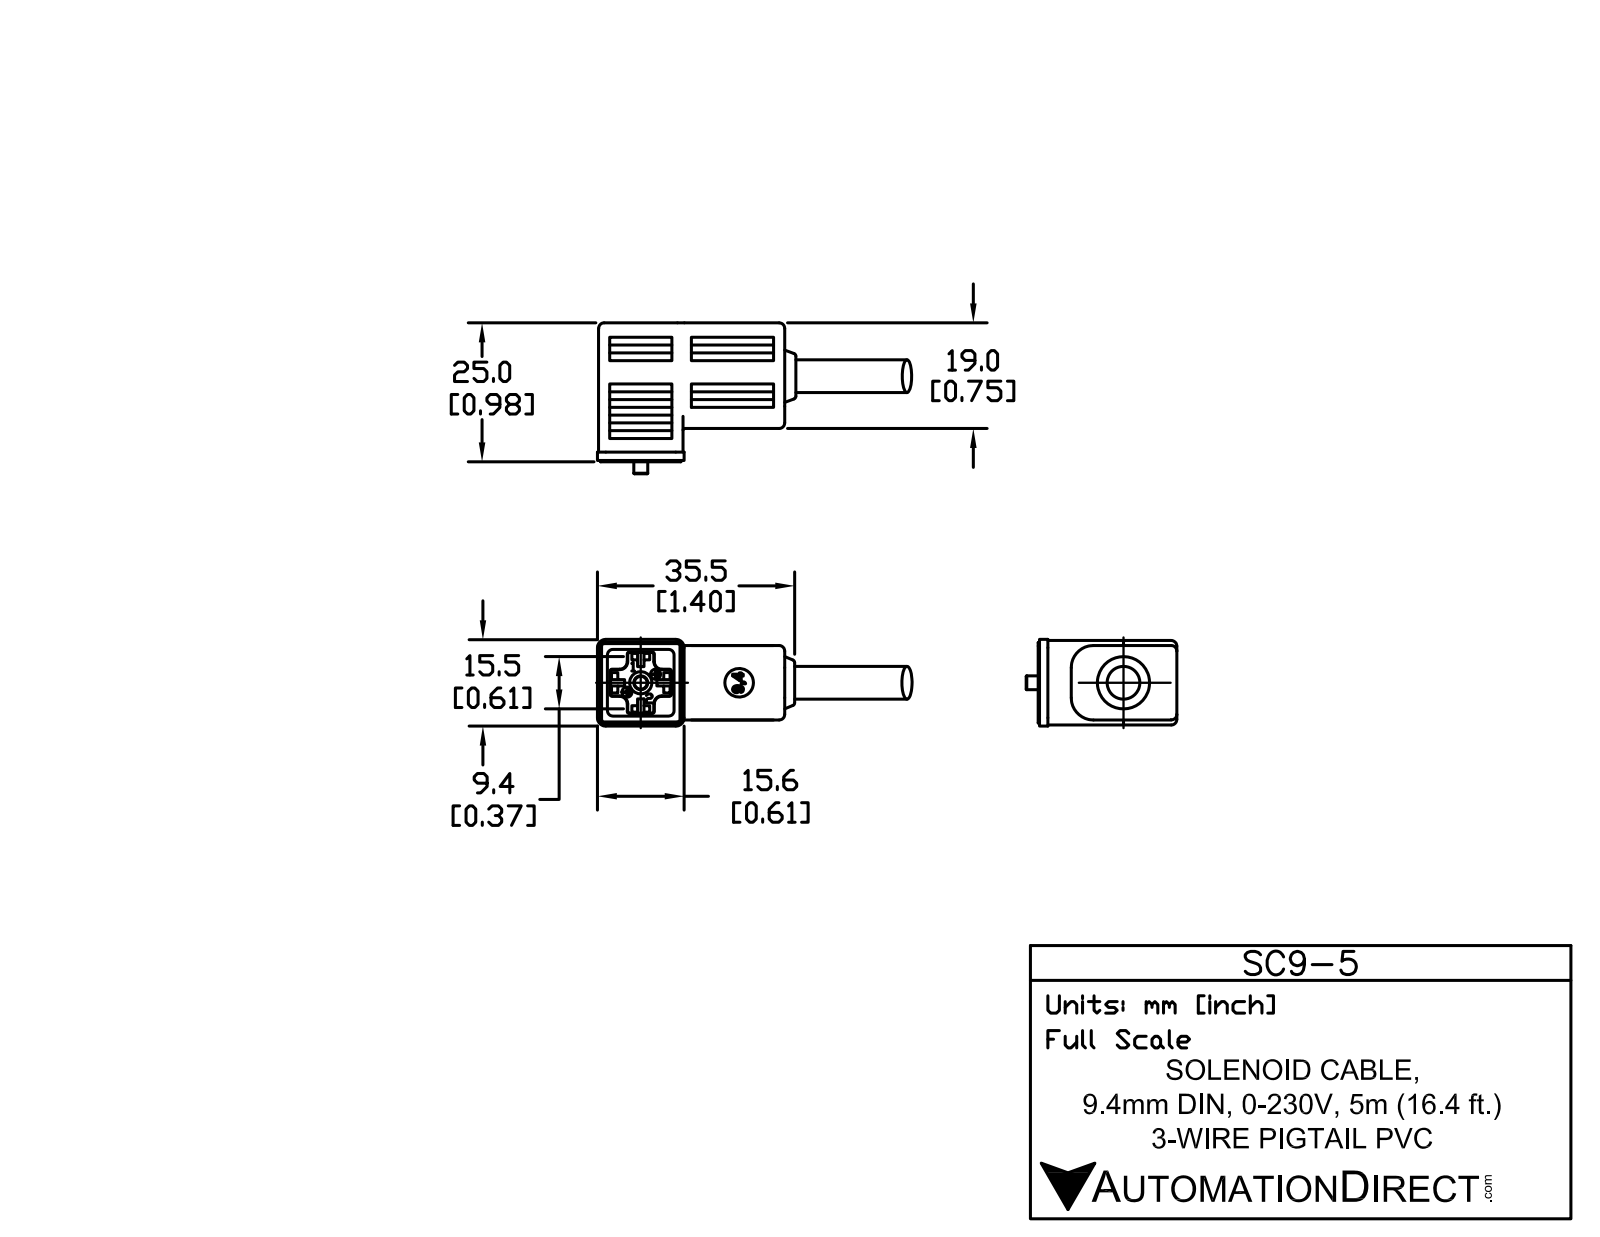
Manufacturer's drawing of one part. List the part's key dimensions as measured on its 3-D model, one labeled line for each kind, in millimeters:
Part name (STEP PRODUCT): SC9-5
STEP written by: SolidWorks 2011 (AUTOMOTIVE_DESIGN)
Units: millimetres
Bodies: 4 solids, 321 faces (255 planar, 35 cylindrical, 31 other)
Overall size (bounding box): 63.37 × 33.61 × 15.77
Volume: 11 179 mm³ · Surface area: 5 685 mm²
Round holes (diameter × count): ⌀2.25 ×2, ⌀6 ×2, ⌀4 ×1
Round bosses / shafts (diameter × count): ⌀5.75 ×1, ⌀2.75 ×1
Partial cylindrical surfaces — rounded edges, fillets, slot ends (radius × count): R0.5 ×10, R0.75 ×4, R2 ×4, R0.25 ×3, R4 ×2
Main face-to-face distances: 22.24, 0.88, 1, 15.5, 23.24, 14.32, 13.75, 0.87, 14.62, 14.63
Hole centre spacings: 3.29, 3.58, 6.5
